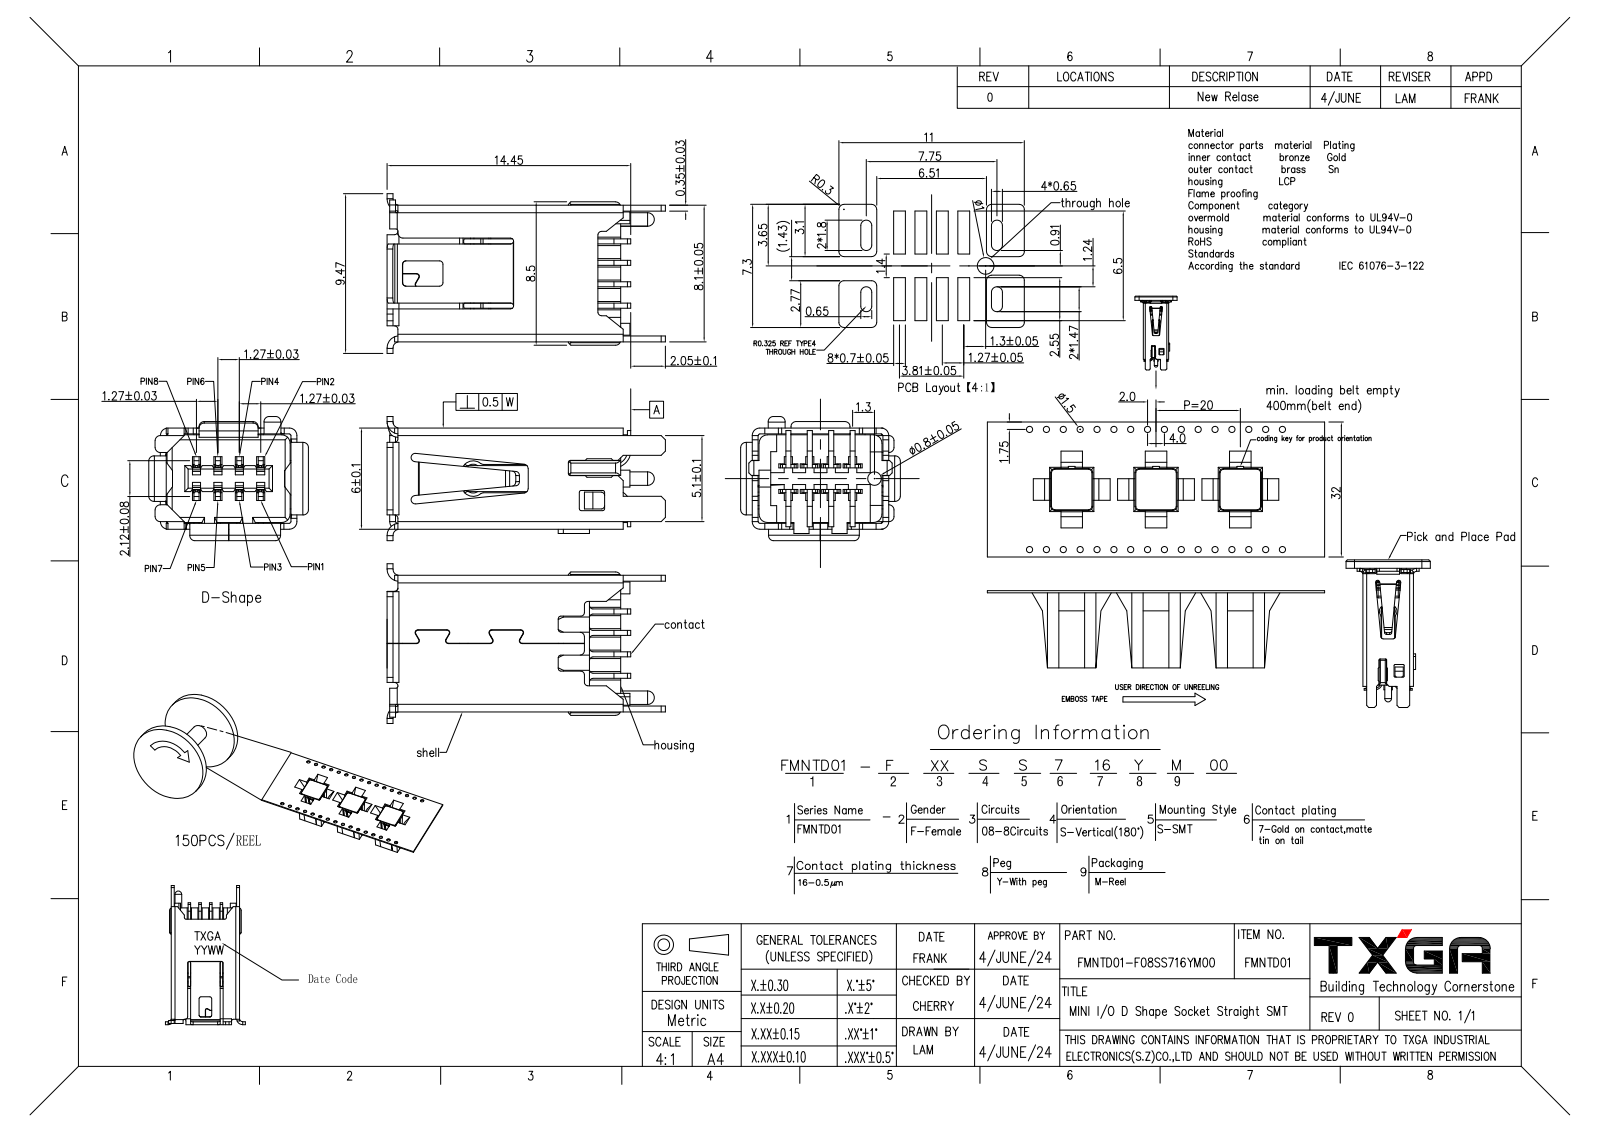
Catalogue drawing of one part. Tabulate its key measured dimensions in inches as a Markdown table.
| quantity | value |
| --- | --- |
| part name | FMINI-SDST1XX-000 |
| STEP written by | PRO/ENGINEER BY PARAMETRIC TECHNOLOGY CORPORATION, 2010280 (CONFIG_CONTROL_DESIGN) |
| units | inches |
| bodies | 1 solid, 1109 faces (785 planar, 322 cylindrical, 2 other) |
| overall size | 0.65 × 0.373 × 0.29 |
| volume | 0.016 in³ |
| surface area | 1.755 in² |
| round bosses / shafts (diameter × count) | 0.031 × 1 |
| partial cylindrical surfaces (radius × count) | 0.004 × 40, 0.006 × 29, 0.008 × 29, 0.012 × 17, 0.01 × 10, 0.028 × 10, 0.007 × 8, 0.014 × 8 |
| main face-to-face distances | 0.014, 0.222, 0.305, 0.236, 0.209, 0.291, 0.016, 0.319, 0.043, 0.262 |
